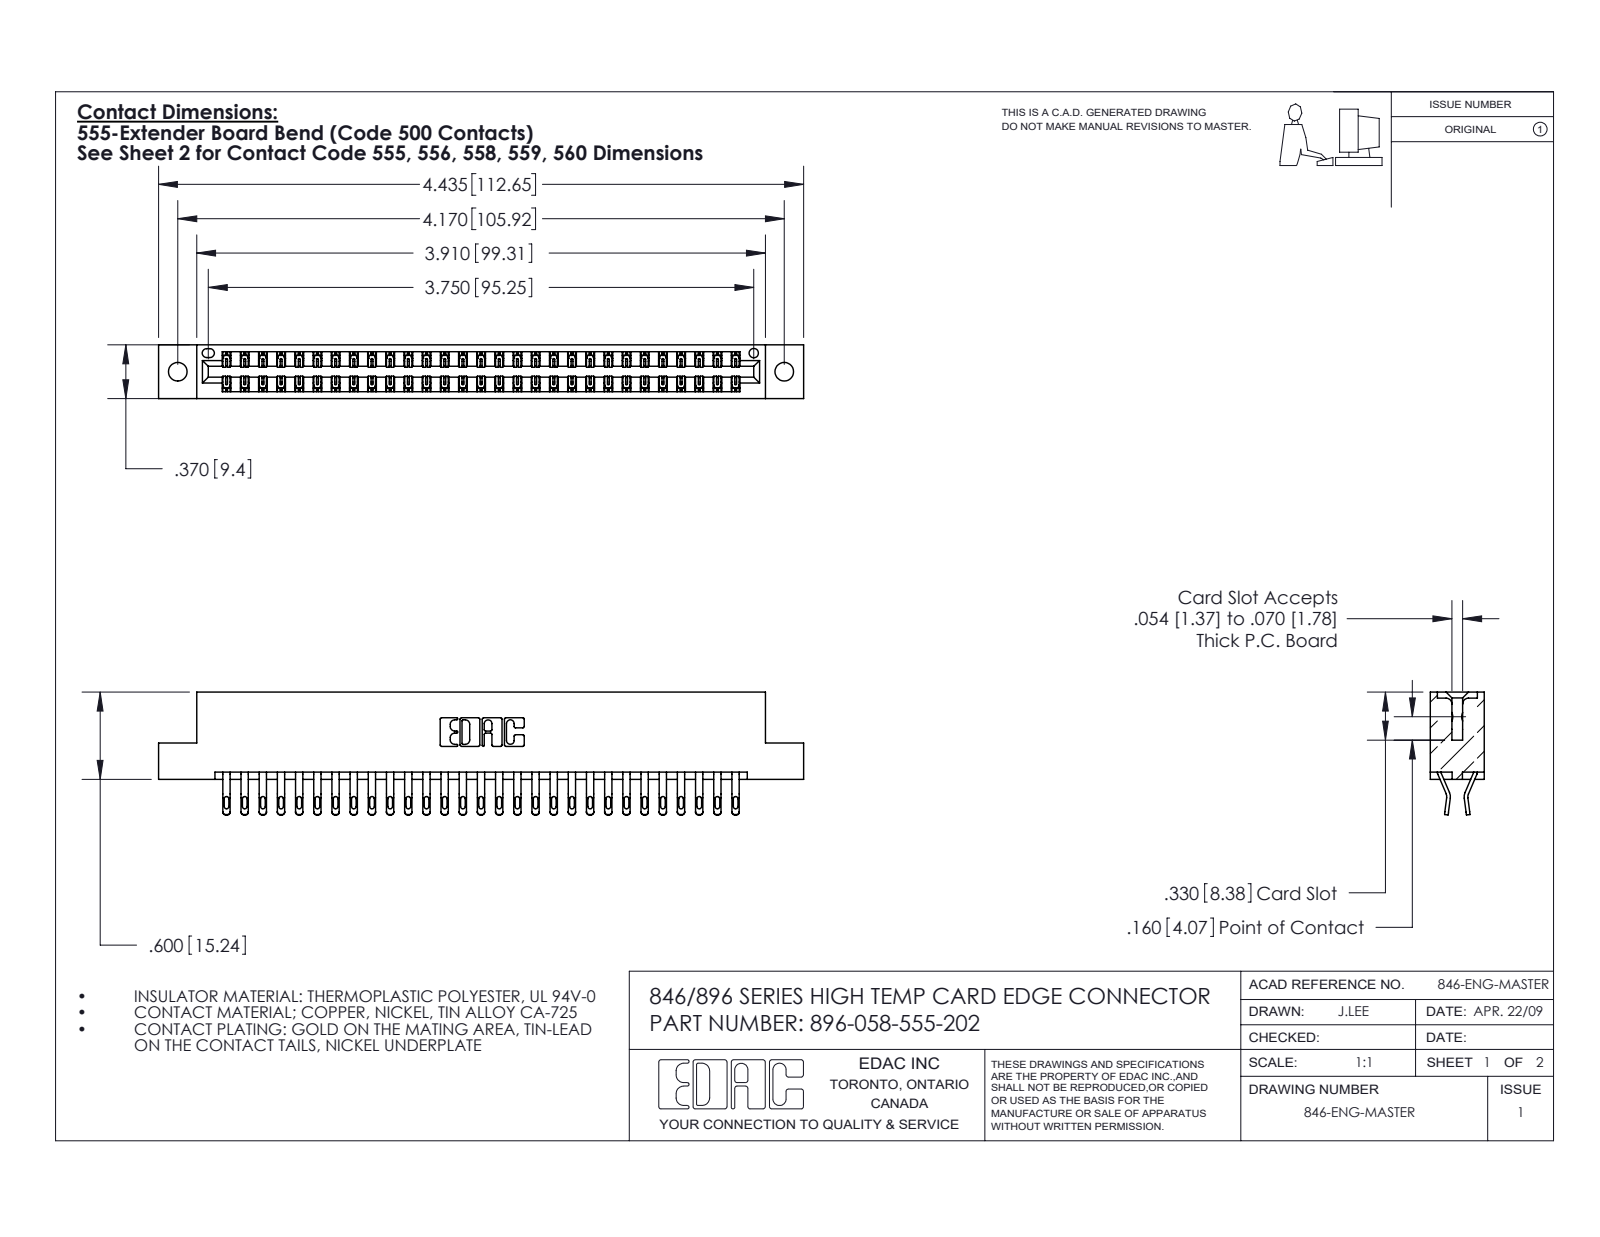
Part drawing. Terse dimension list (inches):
name: 345-292-001_555 Tail; 396-058-555-202; 346 Part_Flush Mounting Lugs - 0.128 Dia
written by: SolidWorks 2016 (CONFIG_CONTROL_DESIGN)
unit: in
bodies: 59 solids, 3486 faces (1990 planar, 1496 cylindrical, 0 other)
size: 4.435 × 0.845 × 0.37
volume: 0.672 in³; area: 23.66 in²
holes: 2× ⌀0.128, 1× ⌀0.064
rounds: 116× R0.016, 116× R0.02, 87× R0.006, 22× R0.01, 6× R0.007, 6× R0.031, 3× R0.026, 2× R0.01
face distances: 0.048, 0.322, 0.37, 0.25, 0.025, 0.072, 0.298, 0.275, 0.148, 0.222
hole spacings: 0.246, 3.962, 4.17
